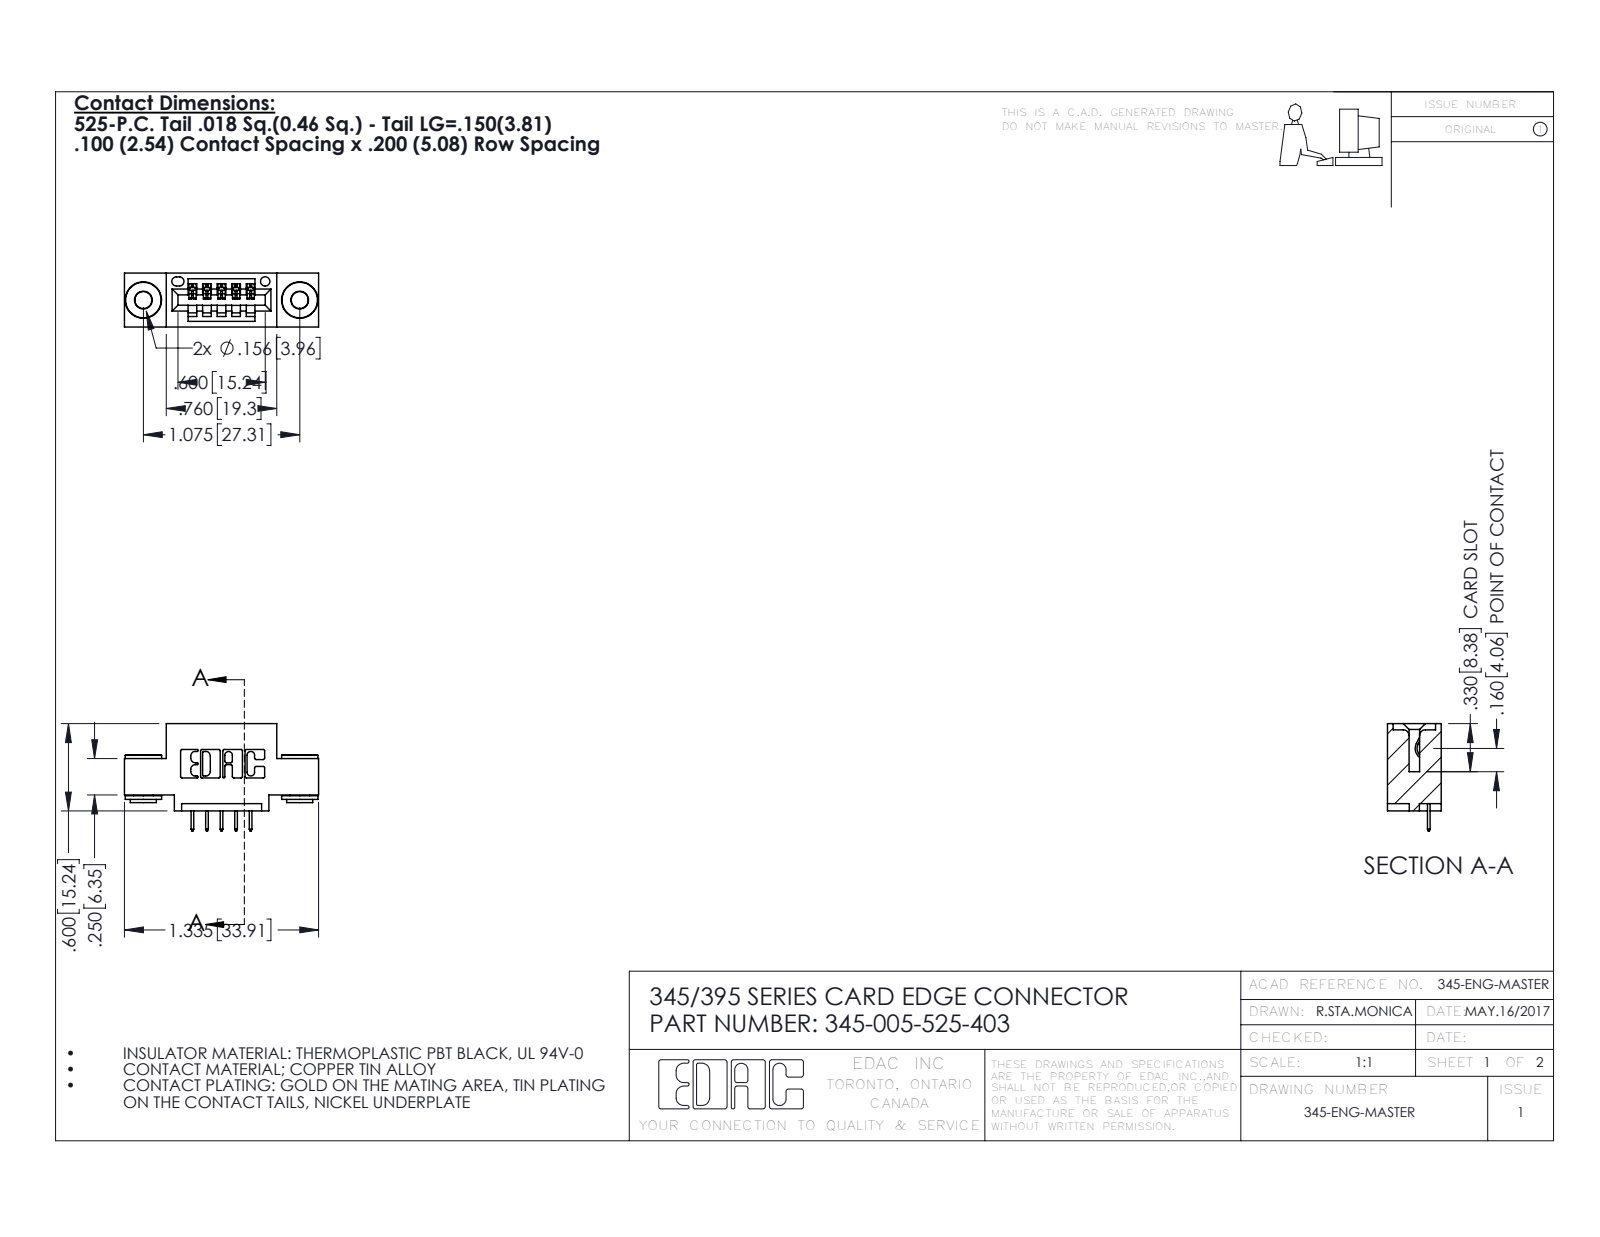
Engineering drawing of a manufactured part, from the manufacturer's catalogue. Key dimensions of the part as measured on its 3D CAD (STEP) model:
Part name (STEP PRODUCT): 345-250-002_345-250-002-102; 345-005-525-403; 345-292-001_345-293-125; 345 Part_0.110 Offset - 0.156 Dia-TH
STEP written by: SolidWorks 2020 (CONFIG_CONTROL_DESIGN)
Units: inches
Bodies: 8 solids, 478 faces (324 planar, 146 cylindrical, 8 other)
Overall size (bounding box): 1.335 × 0.737 × 0.37
Volume: 0.174 in³ · Surface area: 5.431 in²
Round holes (diameter × count): ⌀0.116 ×2, ⌀0.156 ×2, ⌀0.064 ×1
Round bosses / shafts (diameter × count): ⌀0.25 ×2, ⌀0.18 ×2, ⌀0.136 ×2
Partial cylindrical surfaces — rounded edges, fillets, slot ends (radius × count): R0.01 ×22, R0.006 ×10, R0.007 ×6, R0.031 ×6, R0.026 ×3, R0.031 ×2, R0.04 ×2, R0.014 ×1
Main face-to-face distances: 0.37, 0.2, 0.1, 0.072, 0.298, 0.025, 0.25, 0.06, 0.16, 0.55
Hole centre spacings: 0.27, 0.847, 1.075
